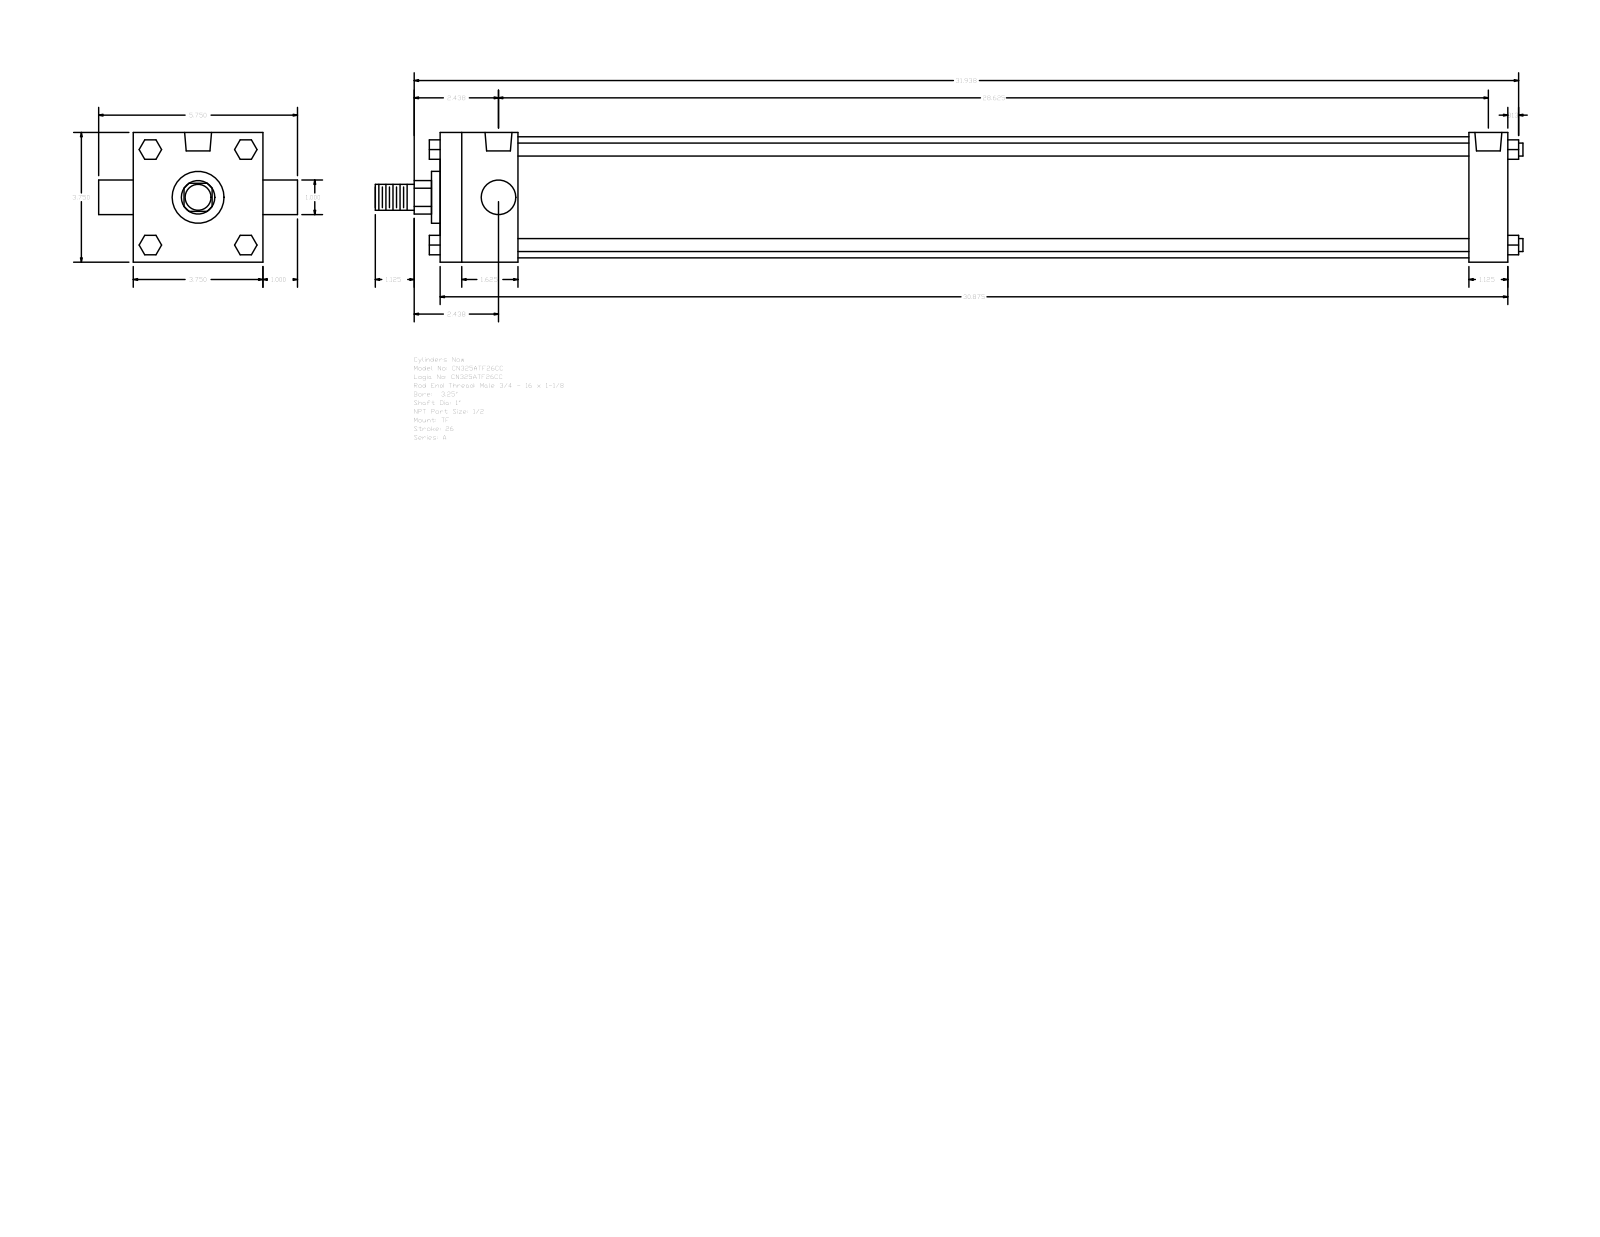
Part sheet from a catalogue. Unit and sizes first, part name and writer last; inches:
Units: inches
Overall size (bounding box): 33.187 × 5.75 × 3.75
Round holes (diameter × count): ⌀0.344 ×3, ⌀0.778 ×2
Round bosses / shafts (diameter × count): ⌀0.375 ×4, ⌀1 ×2, ⌀3.5 ×1, ⌀1.5 ×1, ⌀0.75 ×1
Partial cylindrical surfaces — rounded edges, fillets, slot ends (radius × count): R0.484 ×1
Main face-to-face distances: 3.75, 30.875, 1.125, 2.25, 29.75, 27.5, 28.625, 0.562, 1.38, 2.39
Hole centre spacings: 0.125, 28.5, 28.375, 28.625
Bodies: 0 solids, 120 faces (92 planar, 28 cylindrical, 0 other)
Part name (STEP PRODUCT): A_TF__0325_1
STEP written by: GSSL Pune (CONFIG_CONTROL_DESIGN)
